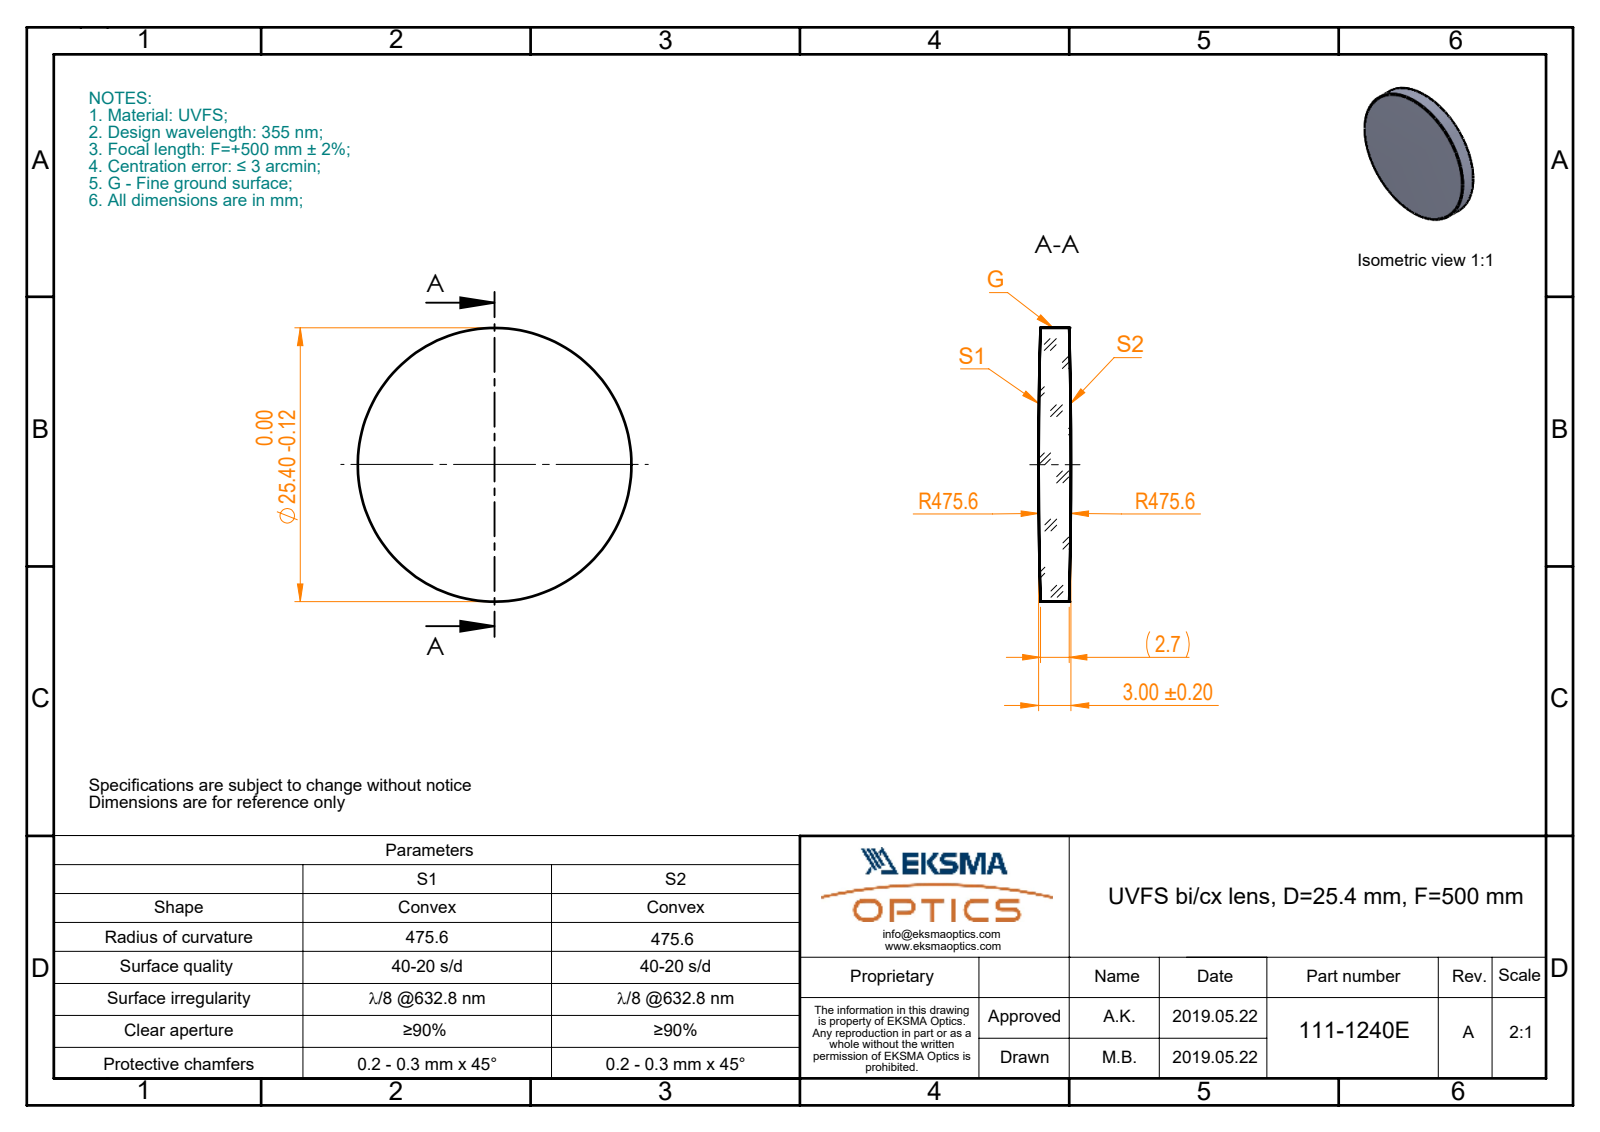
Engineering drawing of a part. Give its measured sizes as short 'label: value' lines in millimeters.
name: 111-1240E UVFS bi-cx 25.4 F500
written by: SolidWorks 2017 (CONFIG_CONTROL_DESIGN)
unit: mm
bodies: 1 solid, 6 faces (0 planar, 2 cylindrical, 4 other)
size: 25.4 × 25.4 × 3
volume: 1 434 mm³; area: 1 226 mm²
bosses: 1× ⌀25.4
